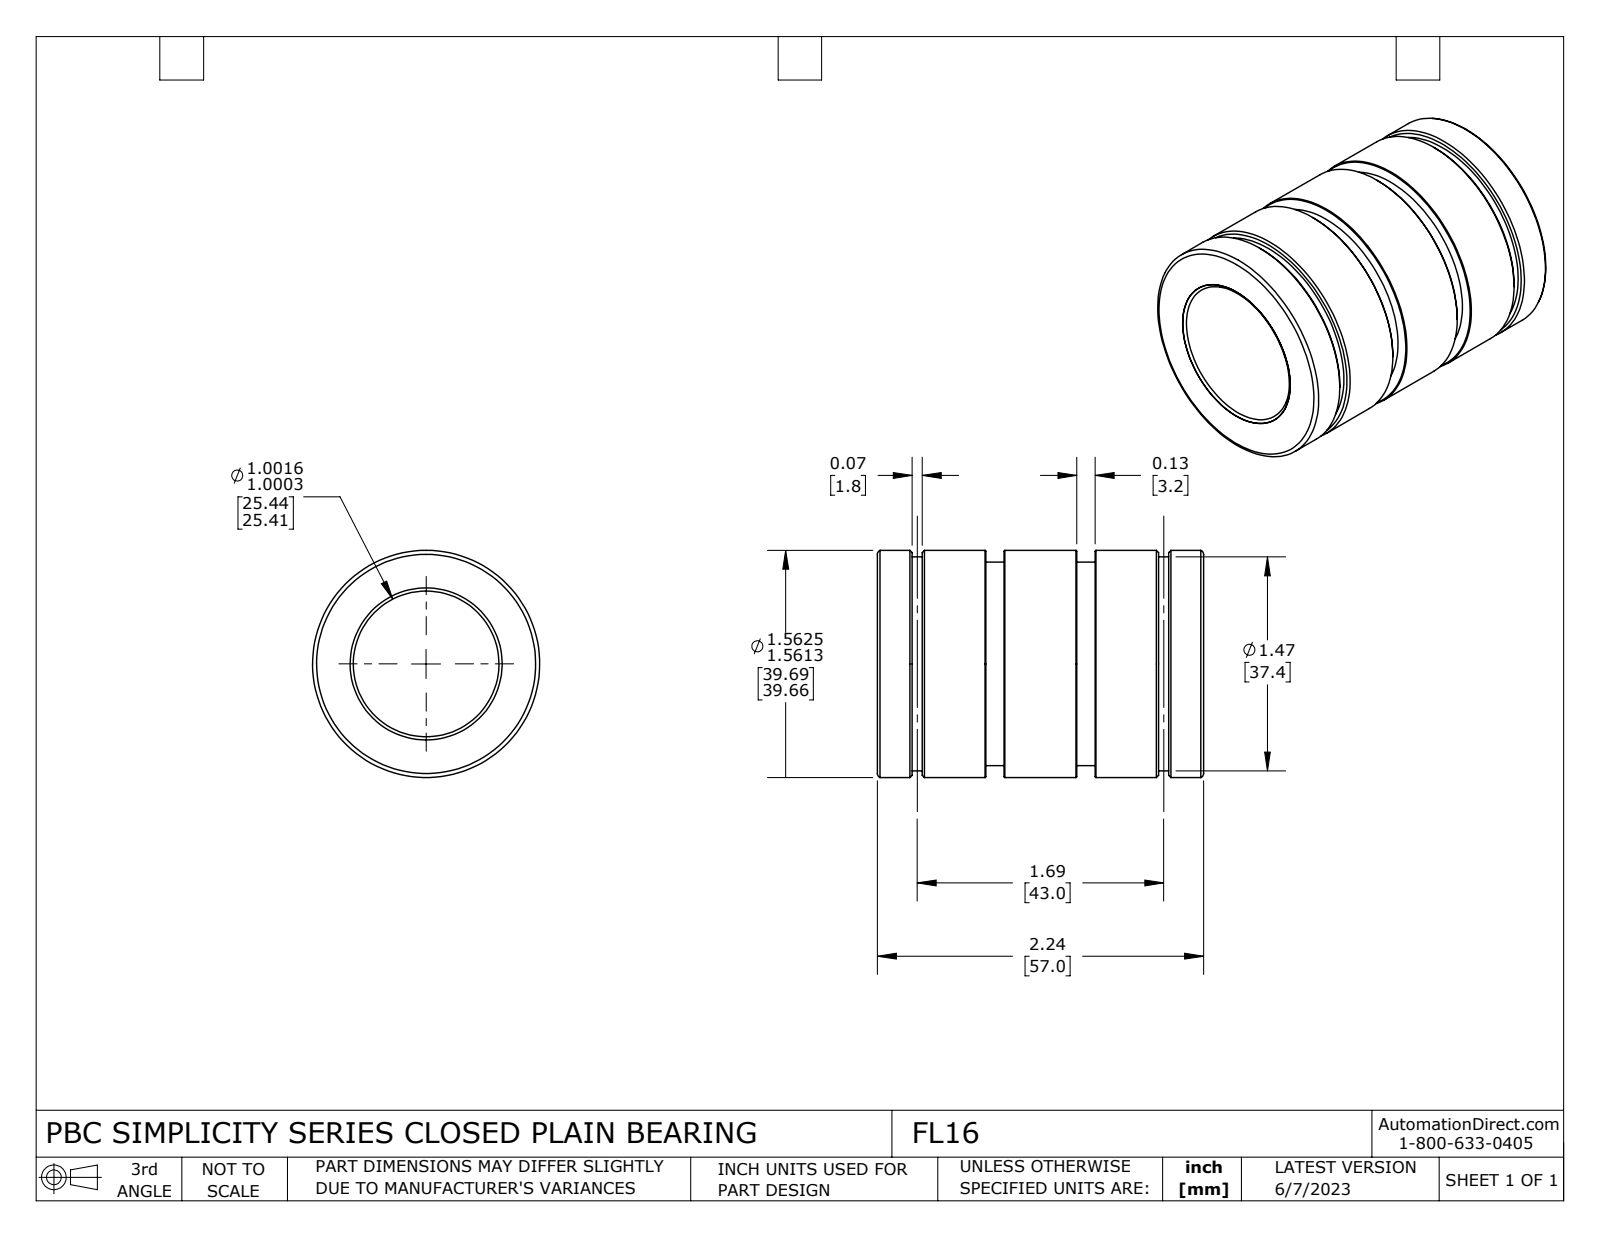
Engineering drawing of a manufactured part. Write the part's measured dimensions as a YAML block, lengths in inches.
part_name: "FL16"
step_written_by: "SolidWorks 2021 (CONFIG_CONTROL_DESIGN)"
units: inches
bodies: {solids: 2, faces: 58, planar: 10, cylindrical: 24, other: 24}
overall_size: [2.242, 1.562, 1.562]
volume: 2.399
surface_area: 36.83
round_holes:
  - {diameter: 1.001, count: 1}
  - {diameter: 1.045, count: 1}
round_bosses_or_shafts:
  - {diameter: 1.562, count: 1}
  - {diameter: 1.471, count: 1}
  - {diameter: 1.399, count: 1}
face_to_face_distances: [2.243, 0.871, 1.371, 0.745, 1.497, 0.126, 0.626, 0.5, 0.752, 0.309]
